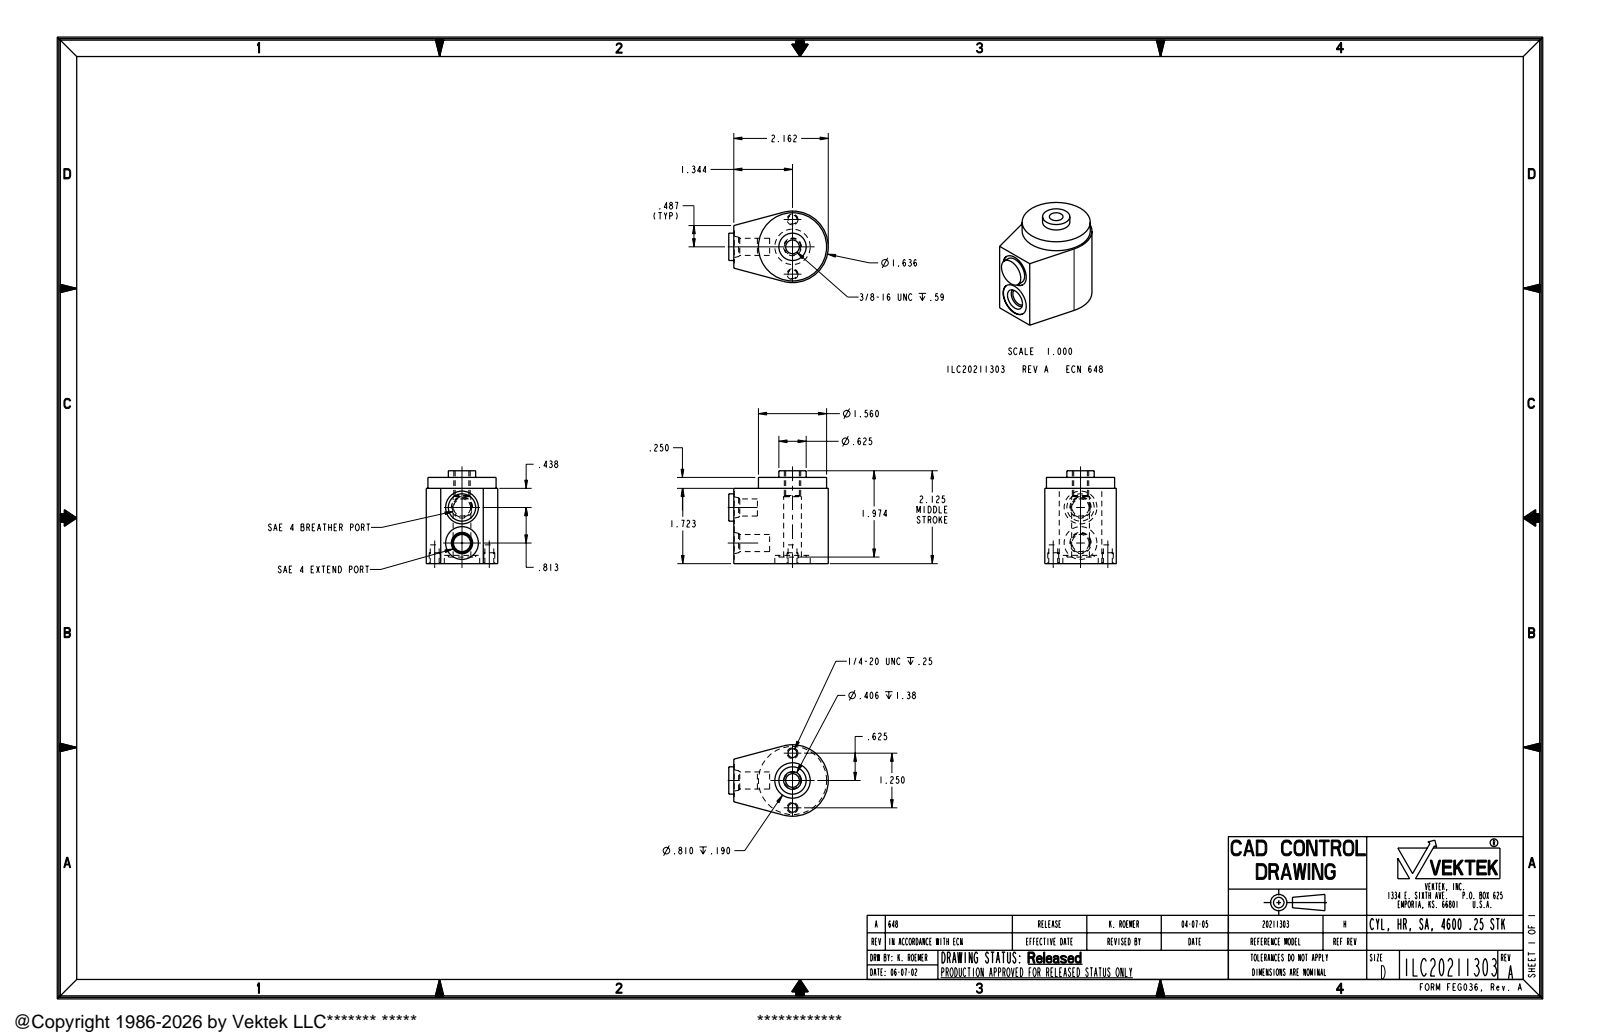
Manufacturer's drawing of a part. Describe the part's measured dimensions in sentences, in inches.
The part is named "ILC20211303". Its 3-D file was written by "PRO/ENGINEER BY PARAMETRIC TECHNOLOGY CORPORATION, 2004290 (AUTOMOTIVE_DESIGN_CC2)". It is 1 solid with 62 faces: 19 planar, 33 cylindrical and 10 other. Overall it measures 2.277 by 2.125 by 1.636 inches. Its volume is 4.935 cubic inches and its surface area 24.75 square inches. Round holes: 2 of diameter 0.204, 2 of diameter 0.392, 2 of diameter 0.75, 1 of diameter 0.313, 1 of diameter 0.406, 1 of diameter 0.81. Round bosses or shafts: 2 of diameter 0.625, 2 of diameter 0.25, 1 of diameter 1.56, 1 of diameter 0.375. Partial cylindrical surfaces (rounded edges, fillets, slot ends): 1 of radius 0.818. The main face-to-face distances are 1.973, 0.25, 1.723, 0.125, 0.115, 2.125, 0.402, 0.152, 0.19, 1.533. The hole center spacings are 0.625, 0.813, 1.25.
